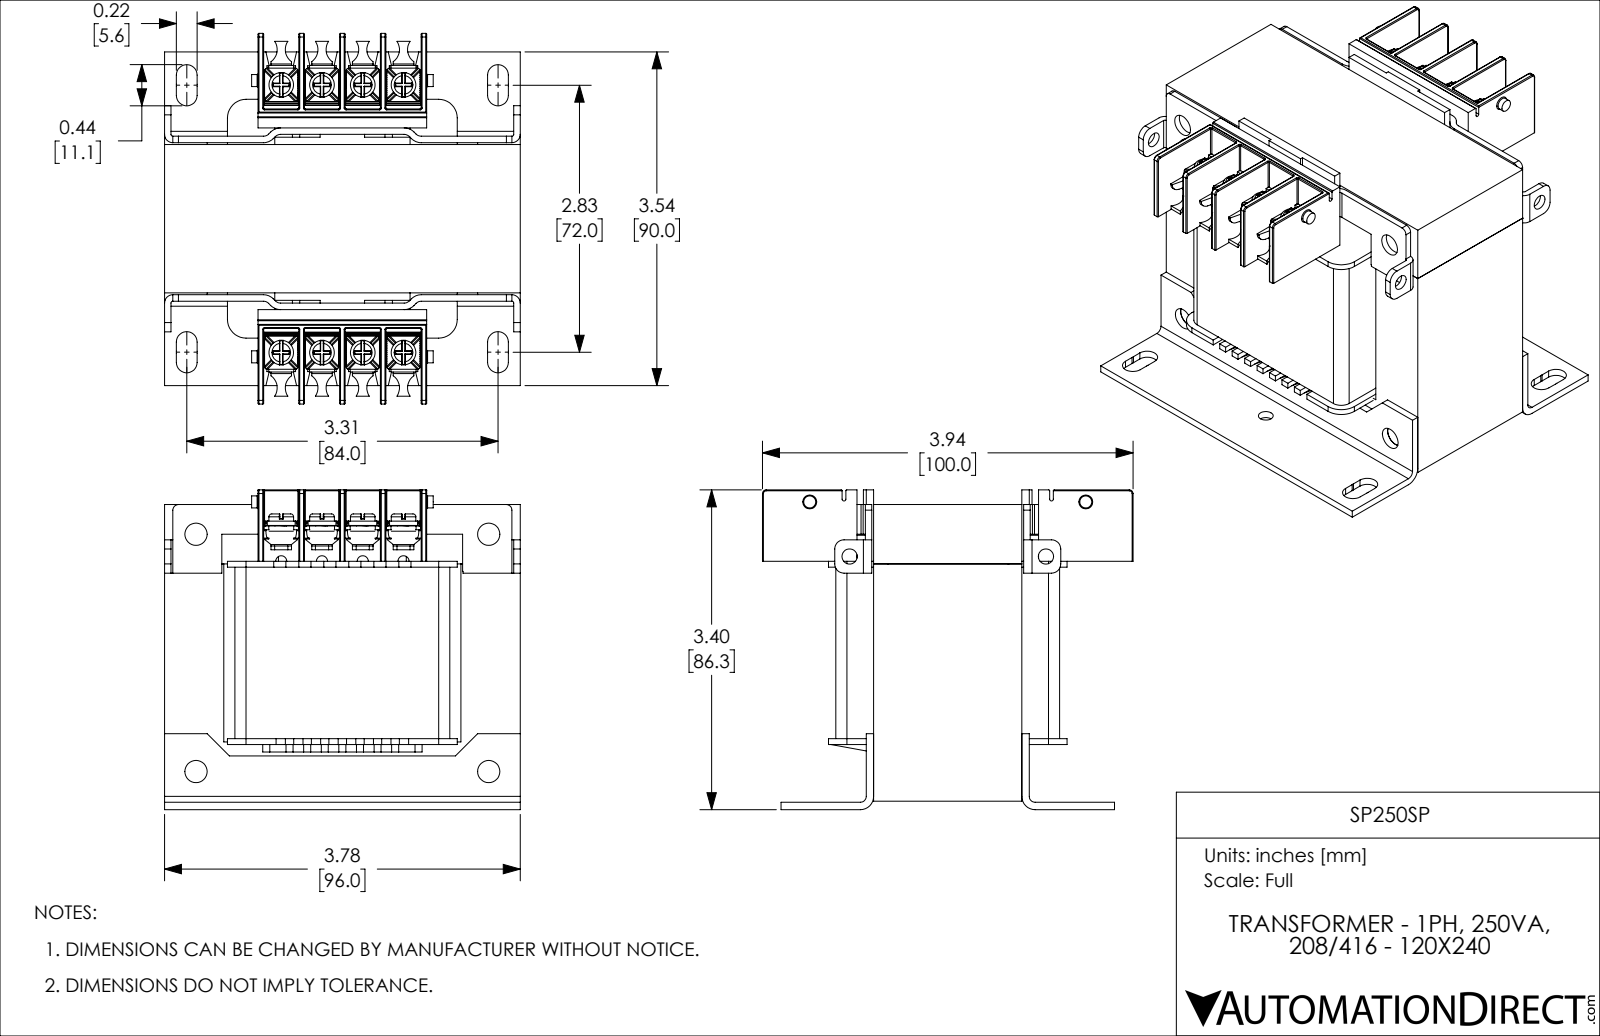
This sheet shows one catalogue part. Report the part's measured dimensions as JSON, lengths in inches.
{"part_name": "SP250SP", "step_written_by": "SolidWorks 2018 (AUTOMOTIVE_DESIGN)", "units": "inches", "bodies": {"solids": 41, "faces": 3218, "planar": 1990, "cylindrical": 930, "other": 298}, "overall_size": [3.937, 3.78, 3.396], "volume_in3": 24.65, "surface_area_in2": 181.7, "round_holes": [[0.157, 10], [0.105, 8], [0.138, 8], [0.236, 4], [0.161, 2]], "round_bosses_or_shafts": [[0.262, 8], [0.24, 8], [0.168, 8], [0.11, 8], [0.128, 2]], "partial_cylinders_radius": [[0.01, 62], [0.005, 52], [0.012, 42], [0.029, 32], [0.157, 16], [0.035, 12], [0.065, 12], [0.079, 10]], "face_to_face_distances": [0.63, 2.52, 1.575, 3.15, 0.079, 1.772, 1.26, 0.059, 1.89, 0.748], "hole_center_spacings": [0.433, 0.866, 2.866, 1.299, 2.833, 2.962, 2.856, 2.875]}
